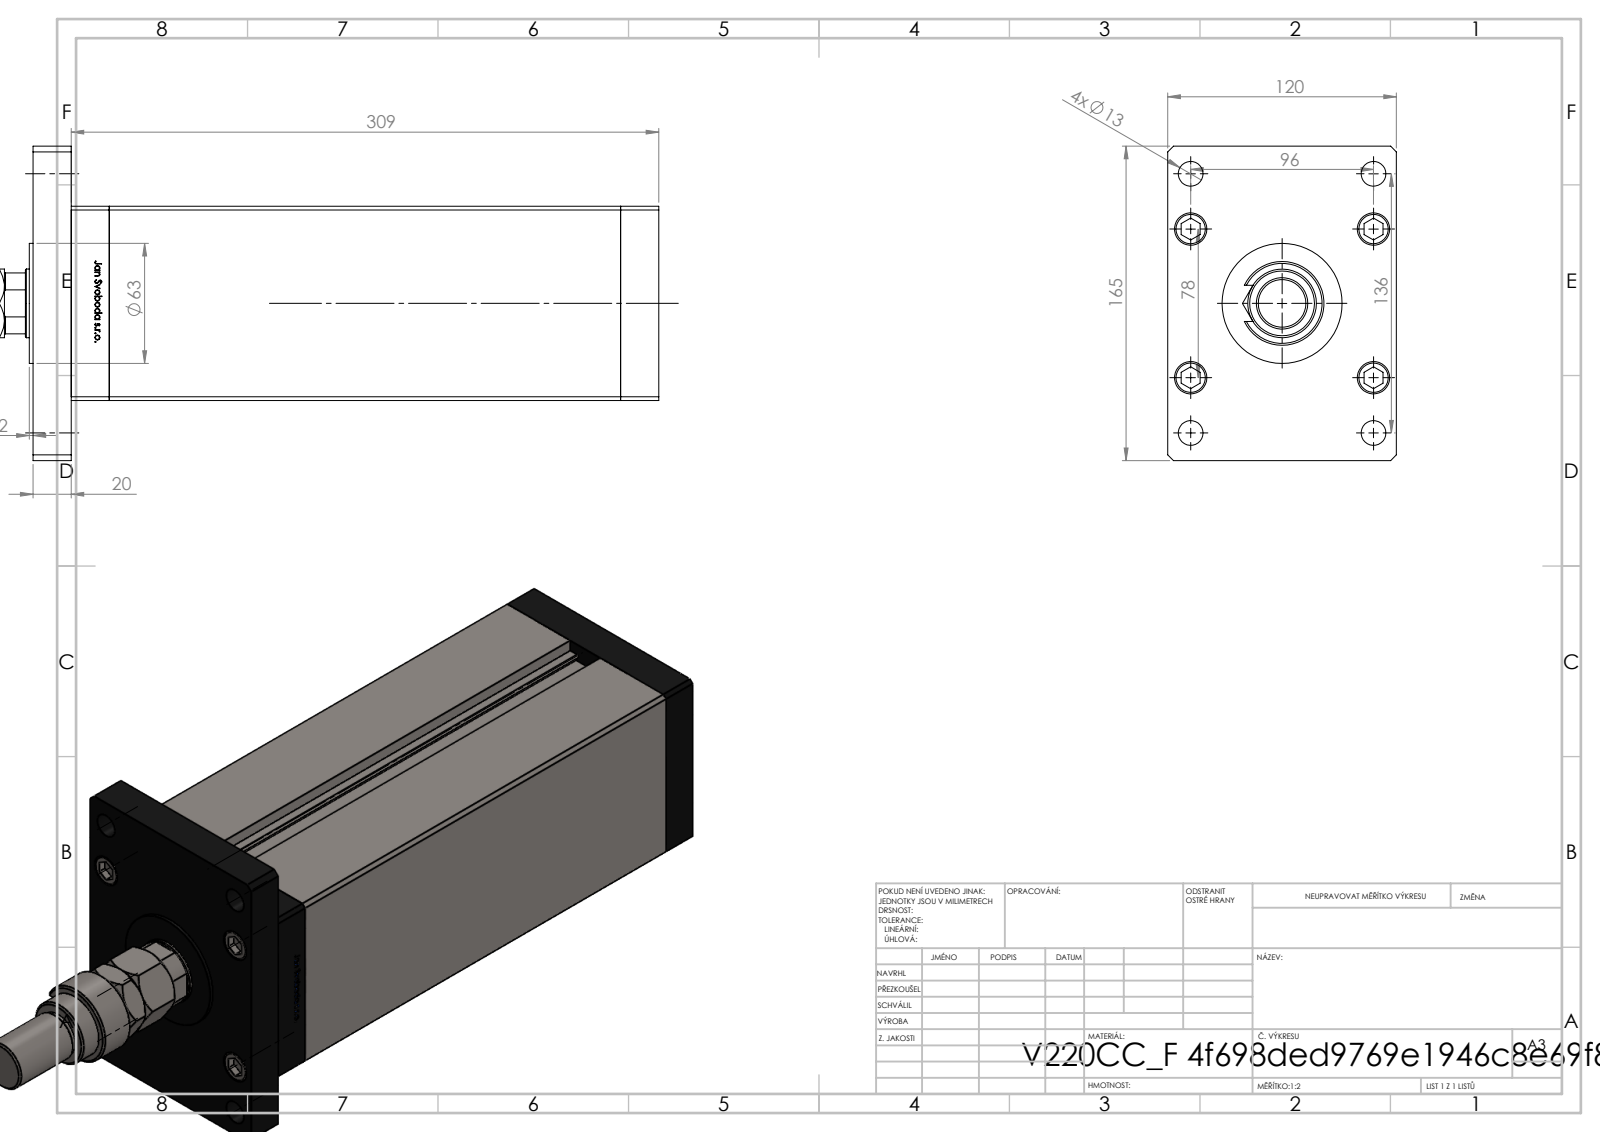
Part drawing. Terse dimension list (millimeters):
name: V220C_F; V220C_FRONT_F; V220C_F_MIDDLE; MFA (+4 more)
written by: SolidWorks 2019 (CONFIG_CONTROL_DESIGN)
unit: mm
bodies: 21 solids, 1396 faces (545 planar, 201 cylindrical, 650 other)
size: 454 × 165 × 120
volume: 3 708 000 mm³; area: 435 510 mm²
holes: 5× ⌀13.5, 5× ⌀18, 4× ⌀12, 4× ⌀13, 4× ⌀17, 2× ⌀2, 2× ⌀13.16, 1× ⌀25.5, 1× ⌀36, 1× ⌀37.5
bosses: 9× ⌀8, 5× ⌀17, 1× ⌀63, 1× ⌀44, 1× ⌀28, 1× ⌀27, 1× ⌀25, 1× ⌀18
rounds: 2× R0.93, 1× R9.5, 1× R15, 1× R17.5
face distances: 20, 120, 102, 288.5, 308.5, 268.5, 40, 328.5, 34.25, 2
hole spacings: 41.5, 29, 61.85, 83.23, 96, 100.28, 107, 143.75
